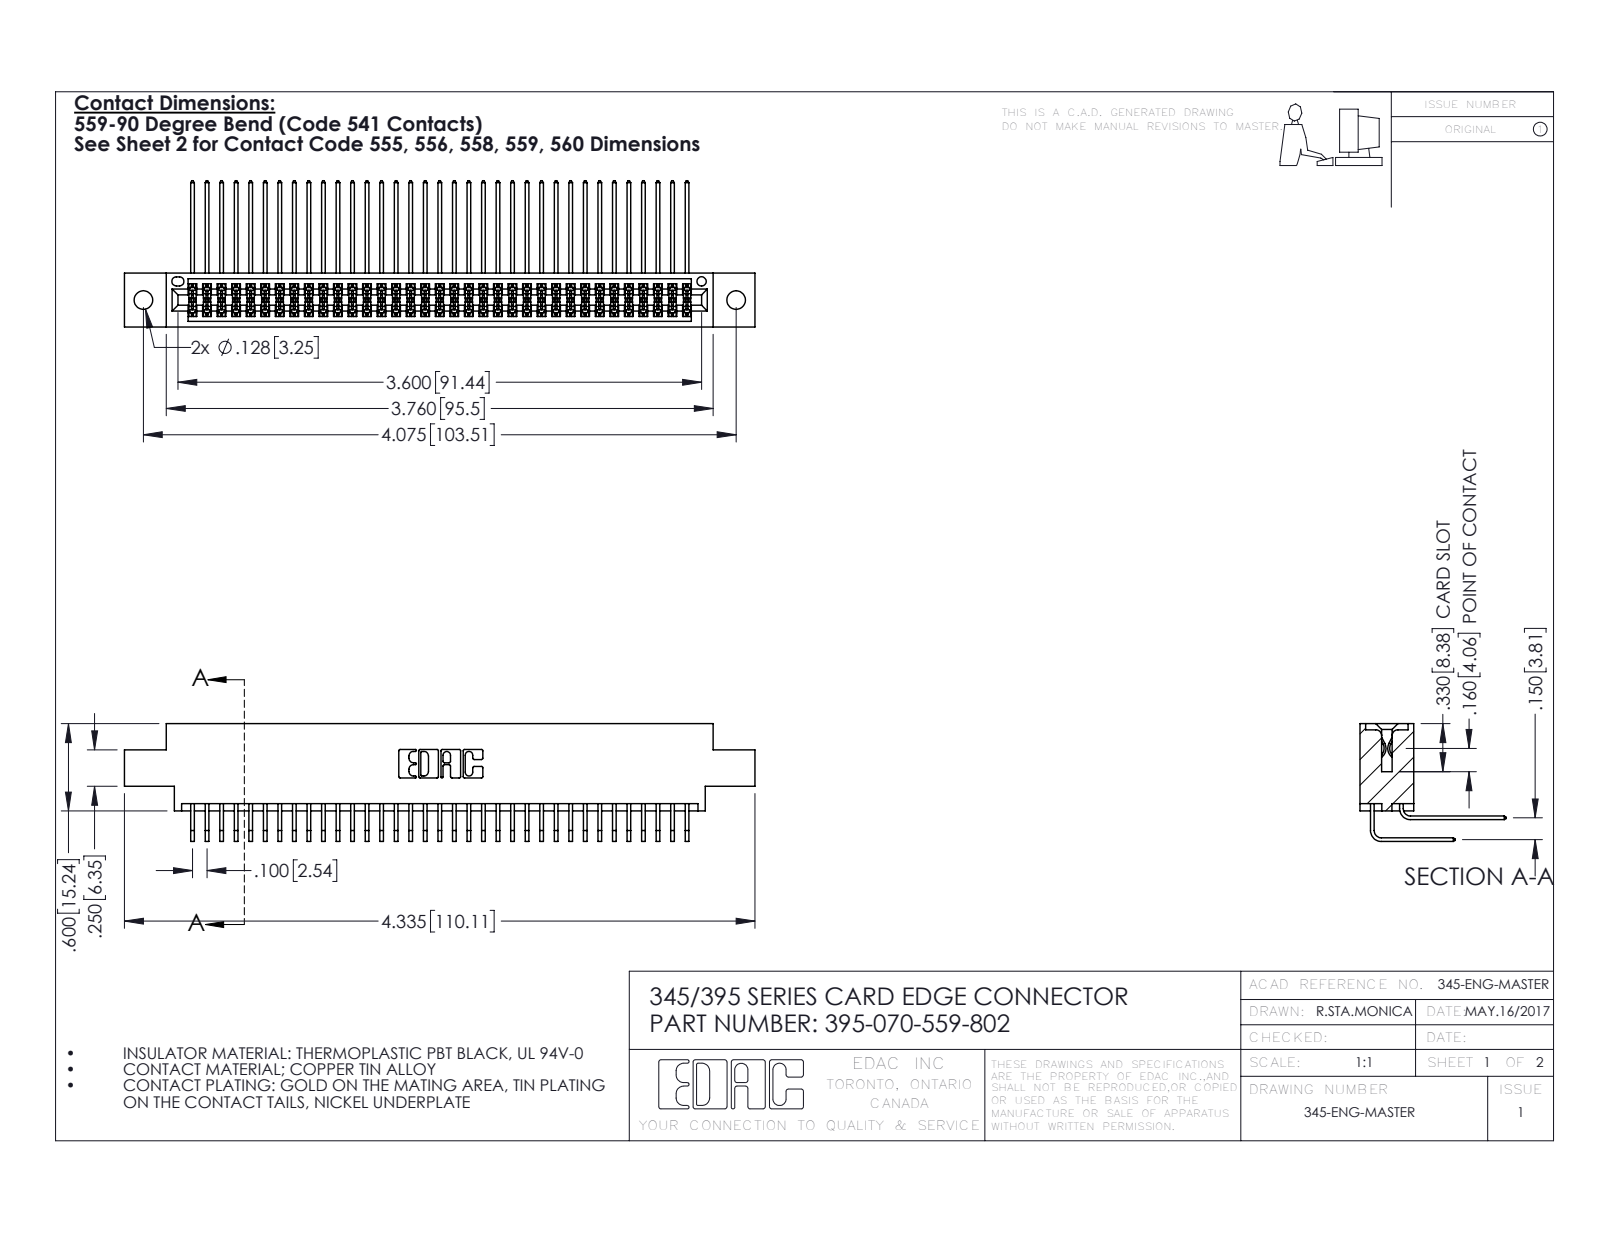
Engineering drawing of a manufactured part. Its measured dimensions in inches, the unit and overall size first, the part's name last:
Units: inches
Overall size (bounding box): 4.335 × 1.005 × 0.809
Round holes (diameter × count): ⌀0.128 ×2, ⌀0.064 ×1
Partial cylindrical surfaces — rounded edges, fillets, slot ends (radius × count): R0.006 ×105, R0.01 ×22, R0.007 ×6, R0.031 ×6, R0.026 ×3, R0.014 ×2, R0.019 ×2, R0.022 ×2
Main face-to-face distances: 0.072, 0.298, 0.37, 0.2, 0.098, 0.272, 0.025, 0.225, 0.175, 0.15
Hole centre spacings: 0.27, 3.839, 4.075
Volume: 0.664 in³ · Surface area: 27.47 in²
Bodies: 71 solids, 3770 faces (2534 planar, 1236 cylindrical, 0 other)
Part name (STEP PRODUCT): 345-292-001_559 Tail - 2; 395-070-559-802; 345-292-001_558 559 Tail - 1; 345 Part_0.170 Offset - 0.128 Dia
STEP written by: SolidWorks 2016 (CONFIG_CONTROL_DESIGN)
